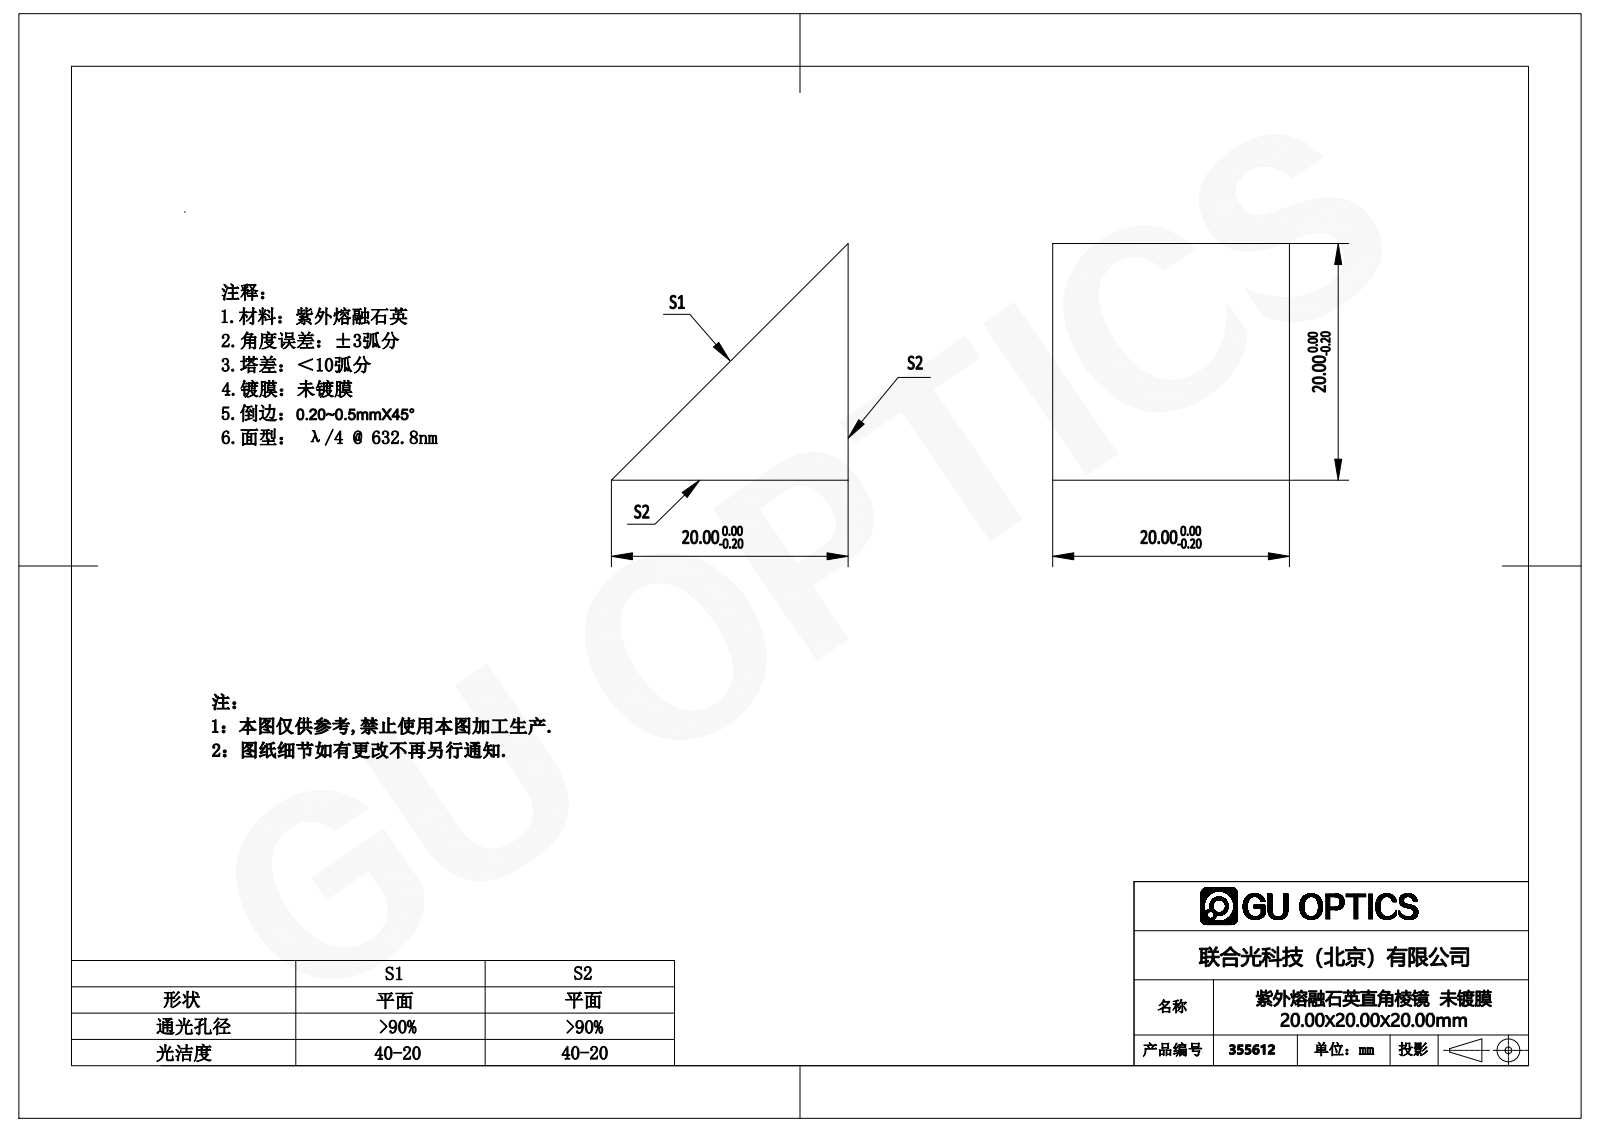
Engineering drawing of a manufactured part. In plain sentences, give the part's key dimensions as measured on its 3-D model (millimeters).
The part is named "355507". Its 3-D file was written by "SolidWorks 2016 (CONFIG_CONTROL_DESIGN)". It is 1 solid with 5 faces: 5 planar, 0 cylindrical and 0 other. Overall it measures 20 by 20 by 20 millimeters. Its volume is 4 000 cubic millimeters and its surface area 1 766 square millimeters. The main face-to-face distances are 20.
